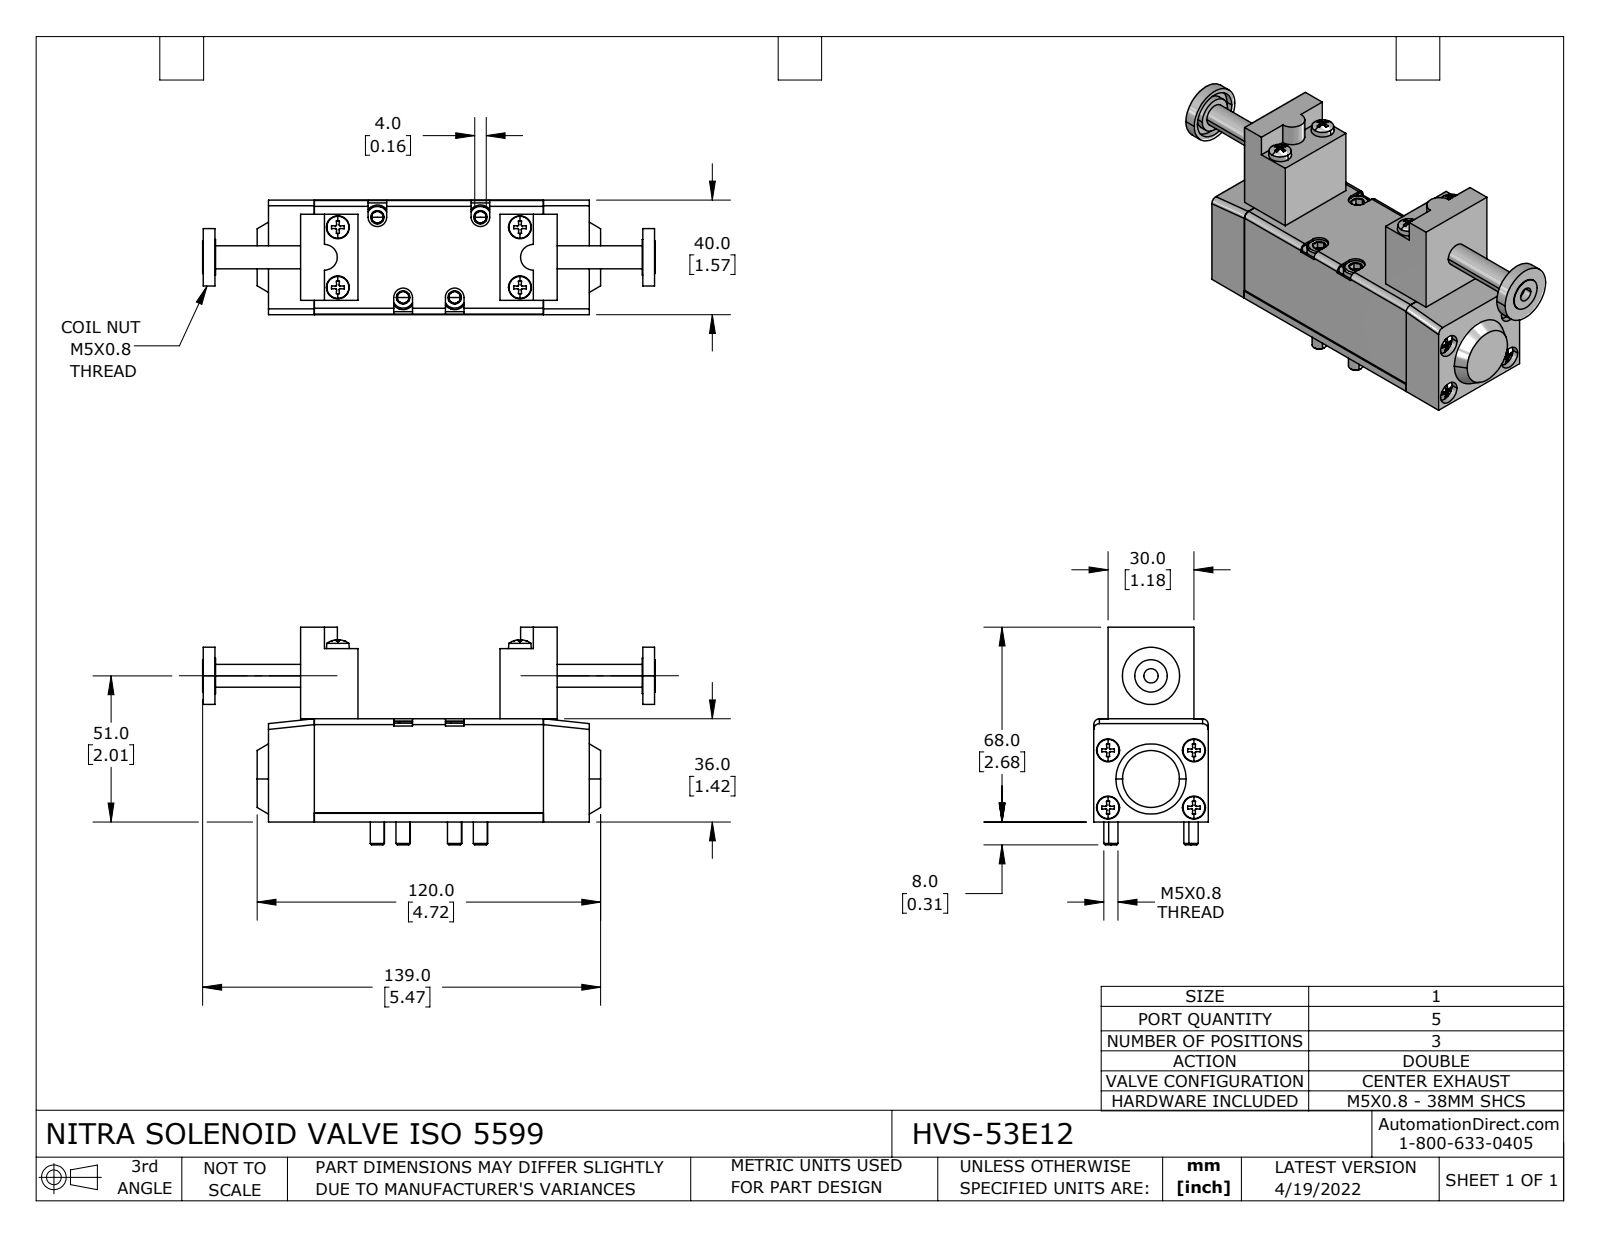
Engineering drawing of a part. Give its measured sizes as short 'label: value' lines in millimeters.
name: HVS-53E12
written by: SolidWorks 2021 (CONFIG_CONTROL_DESIGN)
unit: mm
bodies: 21 solids, 850 faces (434 planar, 156 cylindrical, 260 other)
size: 158 × 76 × 40
volume: 199 600 mm³; area: 54 310 mm²
holes: 8× ⌀3.3, 4× ⌀4.1, 4× ⌀5.5, 4× ⌀8, 1× ⌀5, 1× ⌀16.9
bosses: 8× ⌀4, 4× ⌀8.5, 4× ⌀5, 1× ⌀20, 1× ⌀12.4, 1× ⌀11.3, 1× ⌀8
rounds: 6× R2, 4× R3.3, 4× R5, 2× R4.5
face distances: 4.8, 36, 80, 39.8, 39.6, 84.8, 5, 35, 34.8, 20
hole spacings: 14.2, 20, 21, 23.1, 28.1, 29.4, 30, 30
